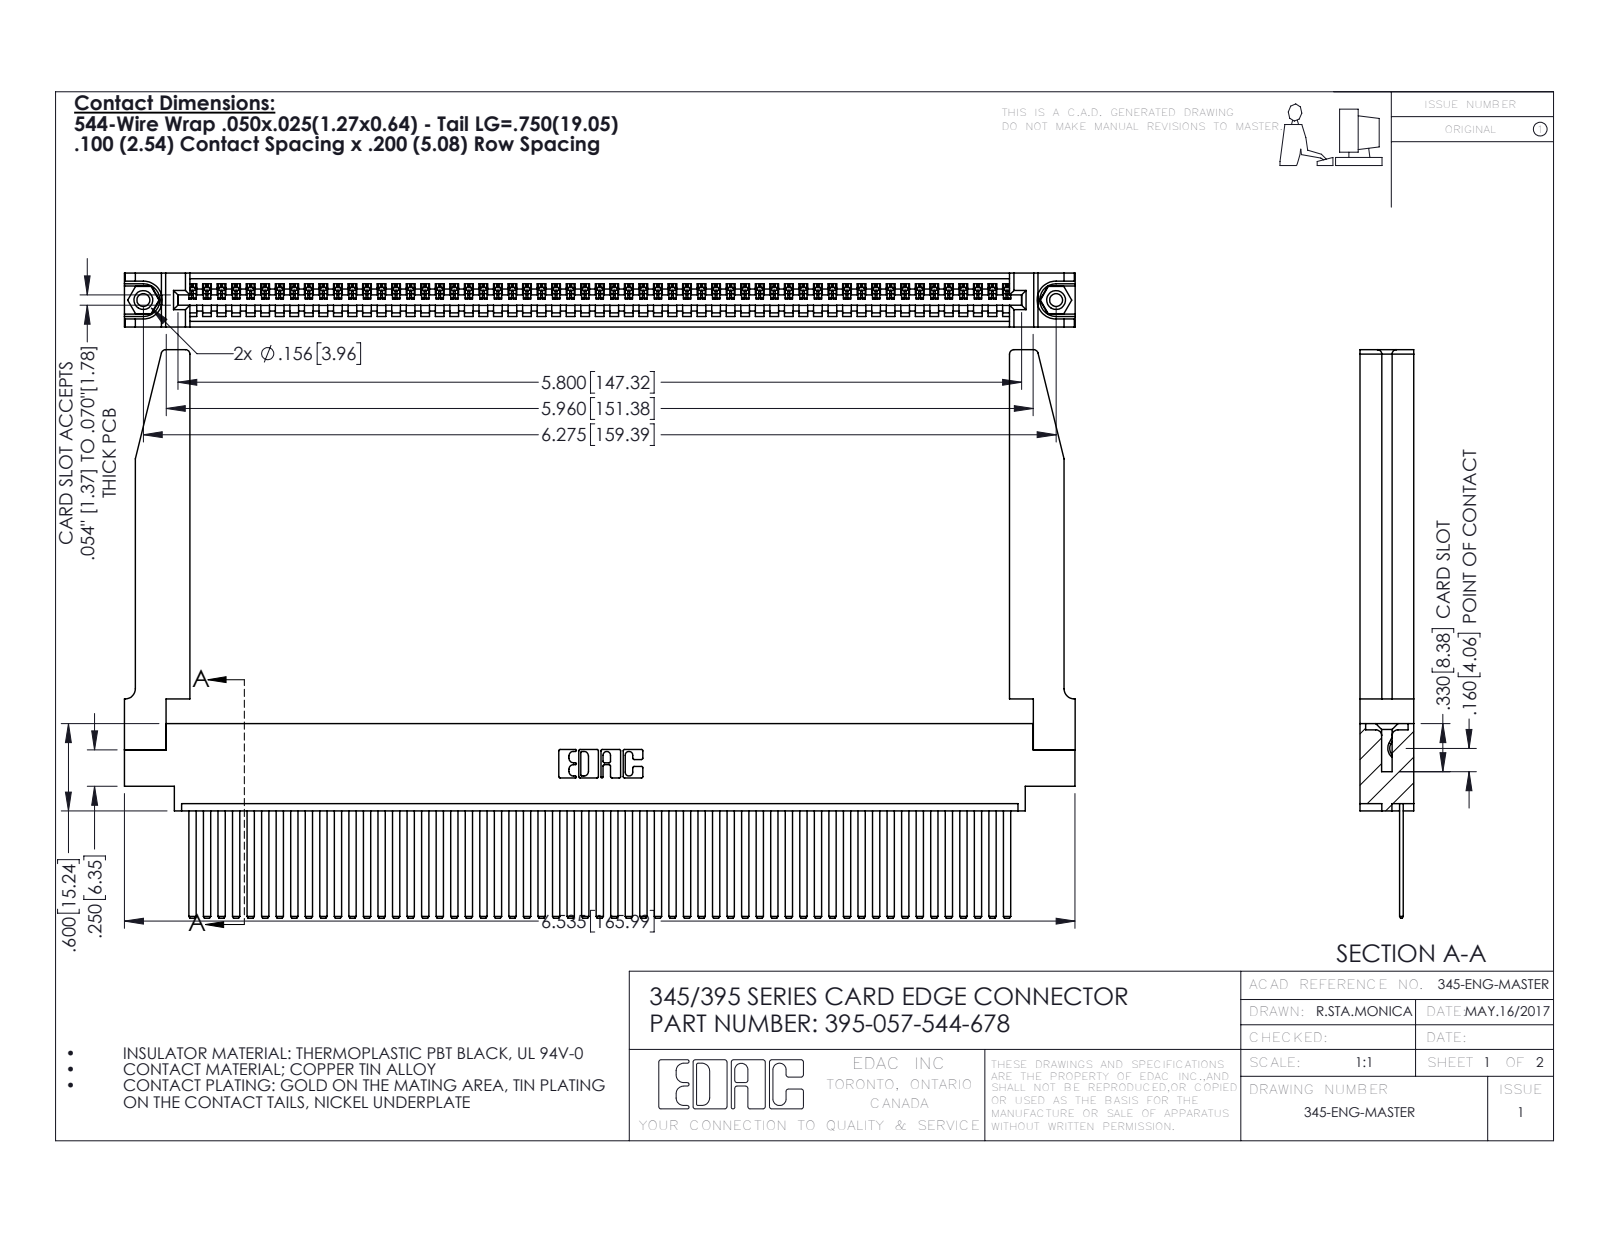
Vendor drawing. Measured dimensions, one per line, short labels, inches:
name: 395-057-544-678; 345 Part_0.170 Offset - 0.156 Dia-TH; 345-220-078_345-220-078; 345-292-001_345-293-144 (+1 more)
written by: SolidWorks 2016 (CONFIG_CONTROL_DESIGN)
unit: in
bodies: 62 solids, 3328 faces (2278 planar, 998 cylindrical, 52 other)
size: 6.536 × 3.907 × 0.37
volume: 1.477 in³; area: 48.05 in²
holes: 2× ⌀0.089, 2× ⌀0.125, 2× ⌀0.156, 1× ⌀0.064
bosses: 2× ⌀0.155
rounds: 114× R0.006, 22× R0.01, 8× R0.03, 6× R0.007, 6× R0.031, 3× R0.026, 2× R0.031, 2× R0.04
face distances: 0.072, 0.298, 0.37, 0.098, 0.272, 0.025, 0.2, 0.225, 0.148, 0.15
hole spacings: 0.27, 6.039, 6.275
